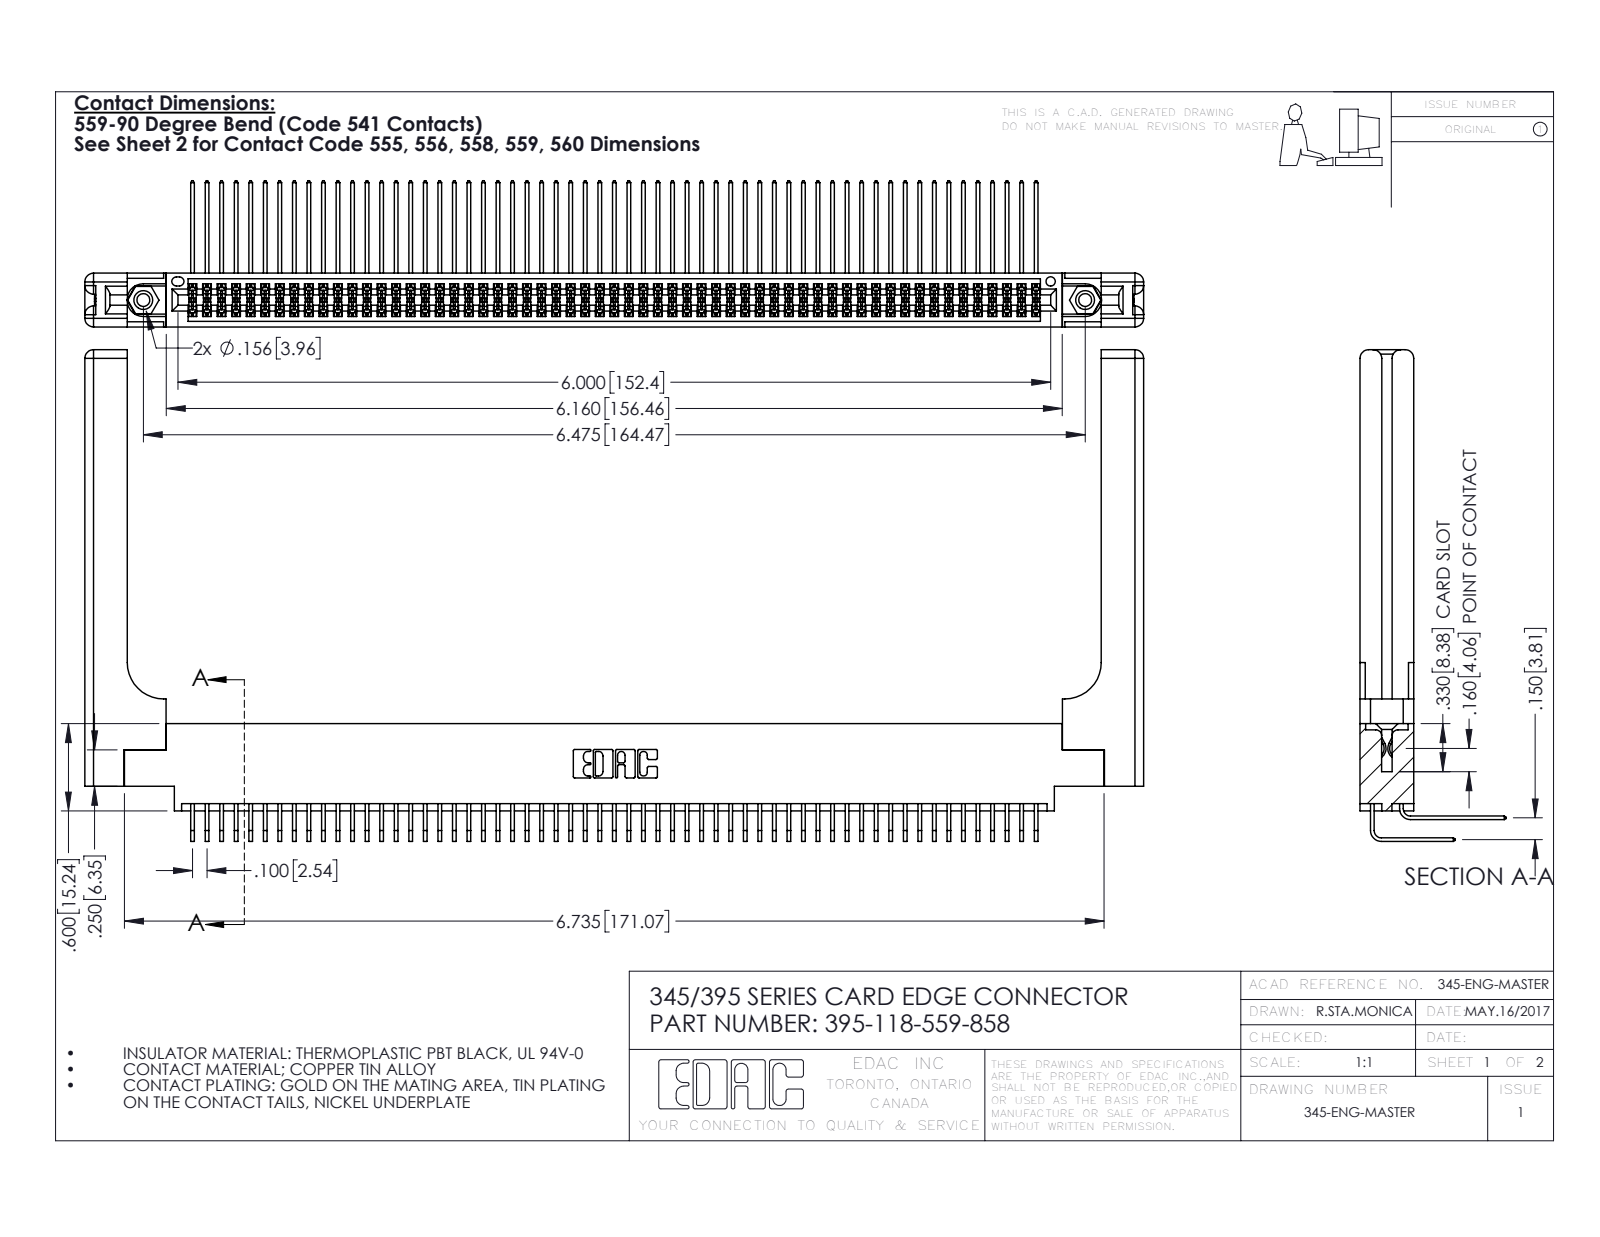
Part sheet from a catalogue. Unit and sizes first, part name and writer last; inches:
Units: inches
Overall size (bounding box): 7.279 × 3.379 × 1.005
Round holes (diameter × count): ⌀0.089 ×2, ⌀0.125 ×2, ⌀0.156 ×2, ⌀0.064 ×1
Round bosses / shafts (diameter × count): ⌀0.155 ×2
Partial cylindrical surfaces — rounded edges, fillets, slot ends (radius × count): R0.006 ×177, R0.01 ×22, R0.06 ×16, R0.007 ×6, R0.031 ×6, R0.026 ×3, R0.014 ×2, R0.019 ×2
Main face-to-face distances: 0.072, 0.298, 0.37, 0.098, 0.272, 0.025, 0.2, 0.225, 0.175, 0.15
Hole centre spacings: 0.27, 6.239, 6.475
Volume: 1.657 in³ · Surface area: 56.35 in²
Bodies: 123 solids, 6522 faces (4362 planar, 2100 cylindrical, 60 other)
Part name (STEP PRODUCT): 345-292-001_558 559 Tail - 1; 345 Part_0.170 Offset - 0.156 Dia-TH; 345-220-058_345-220-058; 345-292-001_559 Tail - 2 (+2 more)
STEP written by: SolidWorks 2016 (CONFIG_CONTROL_DESIGN)
